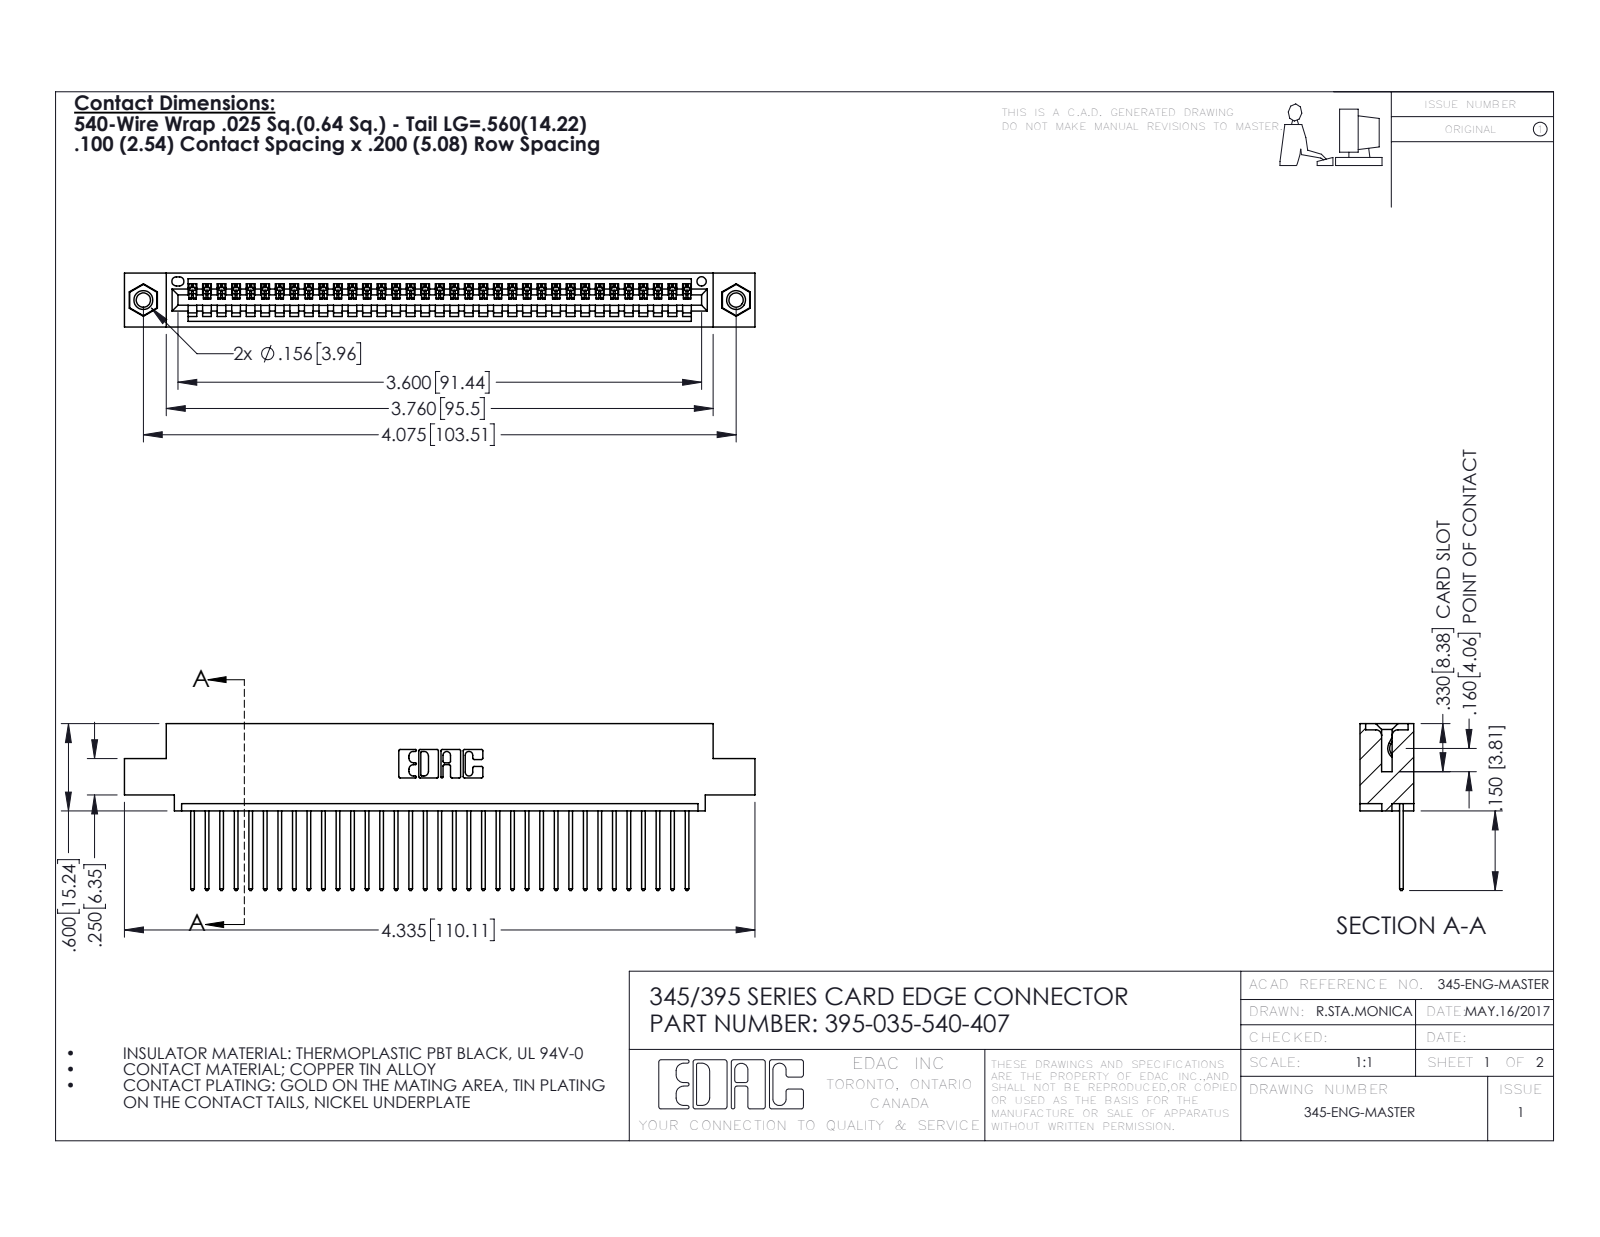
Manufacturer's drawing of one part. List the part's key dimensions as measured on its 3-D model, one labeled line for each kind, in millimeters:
Part name (STEP PRODUCT): 395-035-540-407; 345 Part_0.110 Offset - 0.156 Dia-TI; 345-292-001_345-293-140; 345-250-001_345-250-005-103
STEP written by: SolidWorks 2016 (CONFIG_CONTROL_DESIGN)
Units: millimetres
Bodies: 38 solids, 2220 faces (1516 planar, 688 cylindrical, 16 other)
Overall size (bounding box): 110.1 × 29.1 × 9.4
Volume: 10 400 mm³ · Surface area: 14 130 mm²
Round holes (diameter × count): ⌀2.5 ×2, ⌀3.2 ×2, ⌀4 ×2, ⌀1.6 ×1
Round bosses / shafts (diameter × count): ⌀3.9 ×2
Partial cylindrical surfaces — rounded edges, fillets, slot ends (radius × count): R0.2 ×70, R0.3 ×70, R0.3 ×22, R0.2 ×6, R0.8 ×6, R0.7 ×3, R0.8 ×2, R1 ×2
Main face-to-face distances: 1.8, 7.6, 9.4, 2.5, 6.9, 0.6, 5.1, 5.7, 3.8, 1.8
Hole centre spacings: 6.9, 97.5, 103.5
